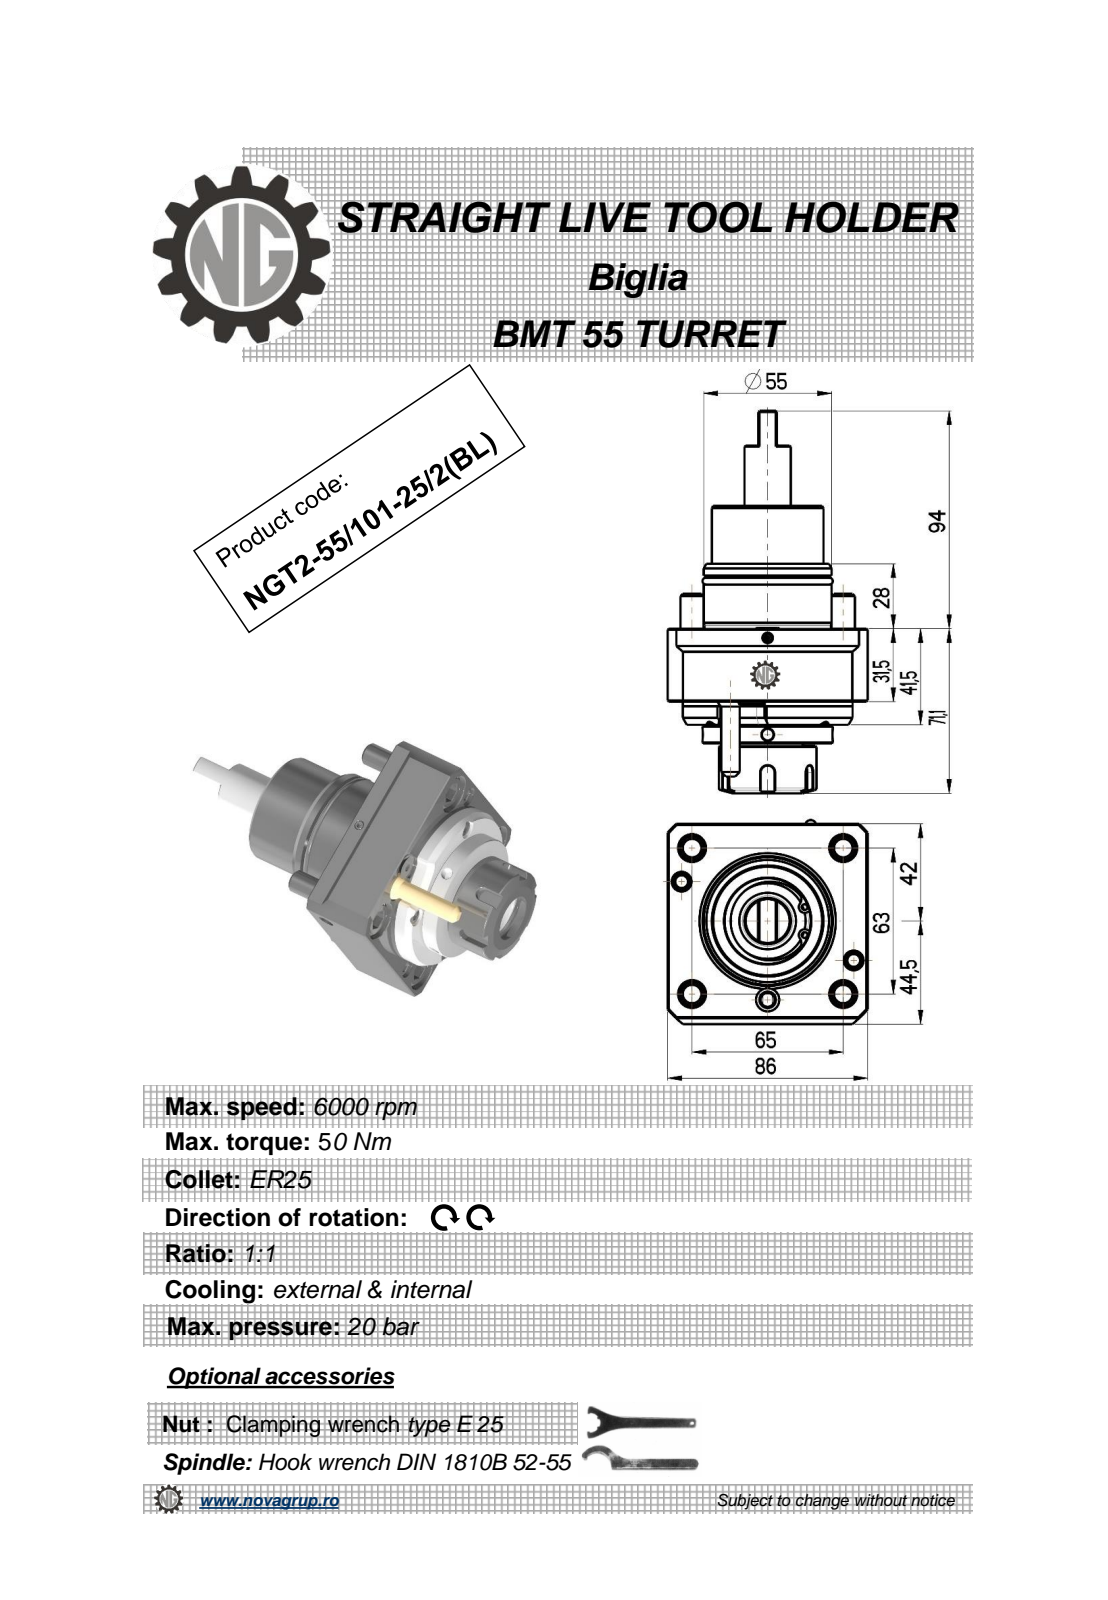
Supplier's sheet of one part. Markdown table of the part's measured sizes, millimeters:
| quantity | value |
| --- | --- |
| part name | NGT2_55_101_25_2_BL |
| STEP written by | PRO/ENGINEER BY PARAMETRIC TECHNOLOGY CORPORATION, 2010280 (CONFIG_CONTROL_DESIGN) |
| units | millimeters |
| bodies | 2 solids, 264 faces (83 planar, 71 cylindrical, 110 other) |
| overall size | 165.1 × 88.1 × 86 |
| volume | 442 665 mm³ |
| surface area | 51 868 mm² |
| round holes (diameter × count) | 5 × 3, 3 × 1, 6 × 1, 20.3 × 1 |
| round bosses / shafts (diameter × count) | 10 × 4, 73 × 1, 56 × 1, 55 × 1, 54.4 × 1, 50 × 1, 48 × 1, 44 × 1 |
| partial cylindrical surfaces (radius × count) | 0.22 × 6, 3 × 5, 0.8 × 2, 6 × 2, 57.5 × 1 |
| main face-to-face distances | 31.5, 86, 41.5, 10, 8, 49.5, 18, 86.5, 53, 84.5 |
| hole center spacings | 16.01, 34, 37.12 |
